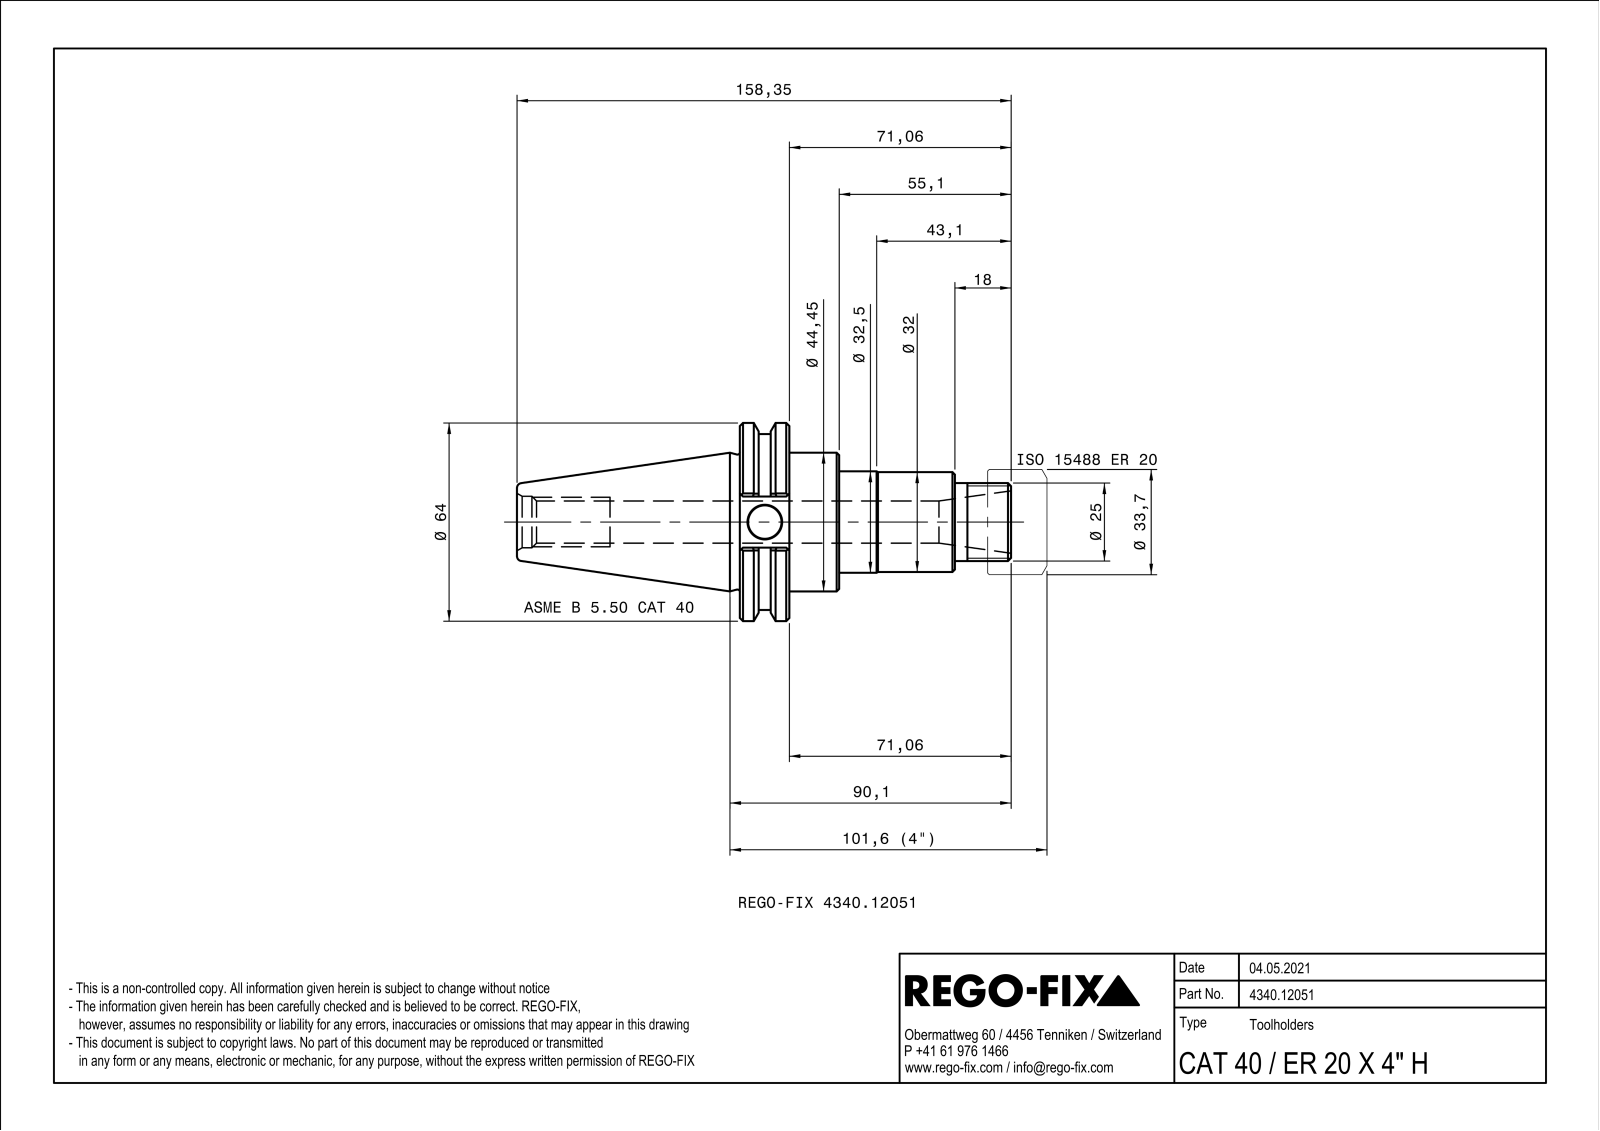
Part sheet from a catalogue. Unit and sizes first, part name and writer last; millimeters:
Units: millimetres
Overall size (bounding box): 158.35 × 63.5 × 60.79
Round holes (diameter × count): ⌀10.7 ×1, ⌀13.5 ×1, ⌀13.53 ×1, ⌀16.5 ×1
Round bosses / shafts (diameter × count): ⌀63.5 ×1, ⌀56.36 ×1, ⌀44.45 ×1, ⌀32.5 ×1, ⌀32 ×1, ⌀25 ×1
Partial cylindrical surfaces — rounded edges, fillets, slot ends (radius × count): R0.5 ×4
Main face-to-face distances: 15.87, 15.96, 31.83, 37.1, 53.06, 68.93, 47.33, 16.38, 140.35, 103.25
Volume: 151 275 mm³ · Surface area: 30 465 mm²
Bodies: 1 solid, 101 faces (32 planar, 22 cylindrical, 47 other)
Part name (STEP PRODUCT): NOCUT
STEP written by: SIEMENS PLM Software Solid Edge ST10 (AUTOMOTIVE_DESIGN)
